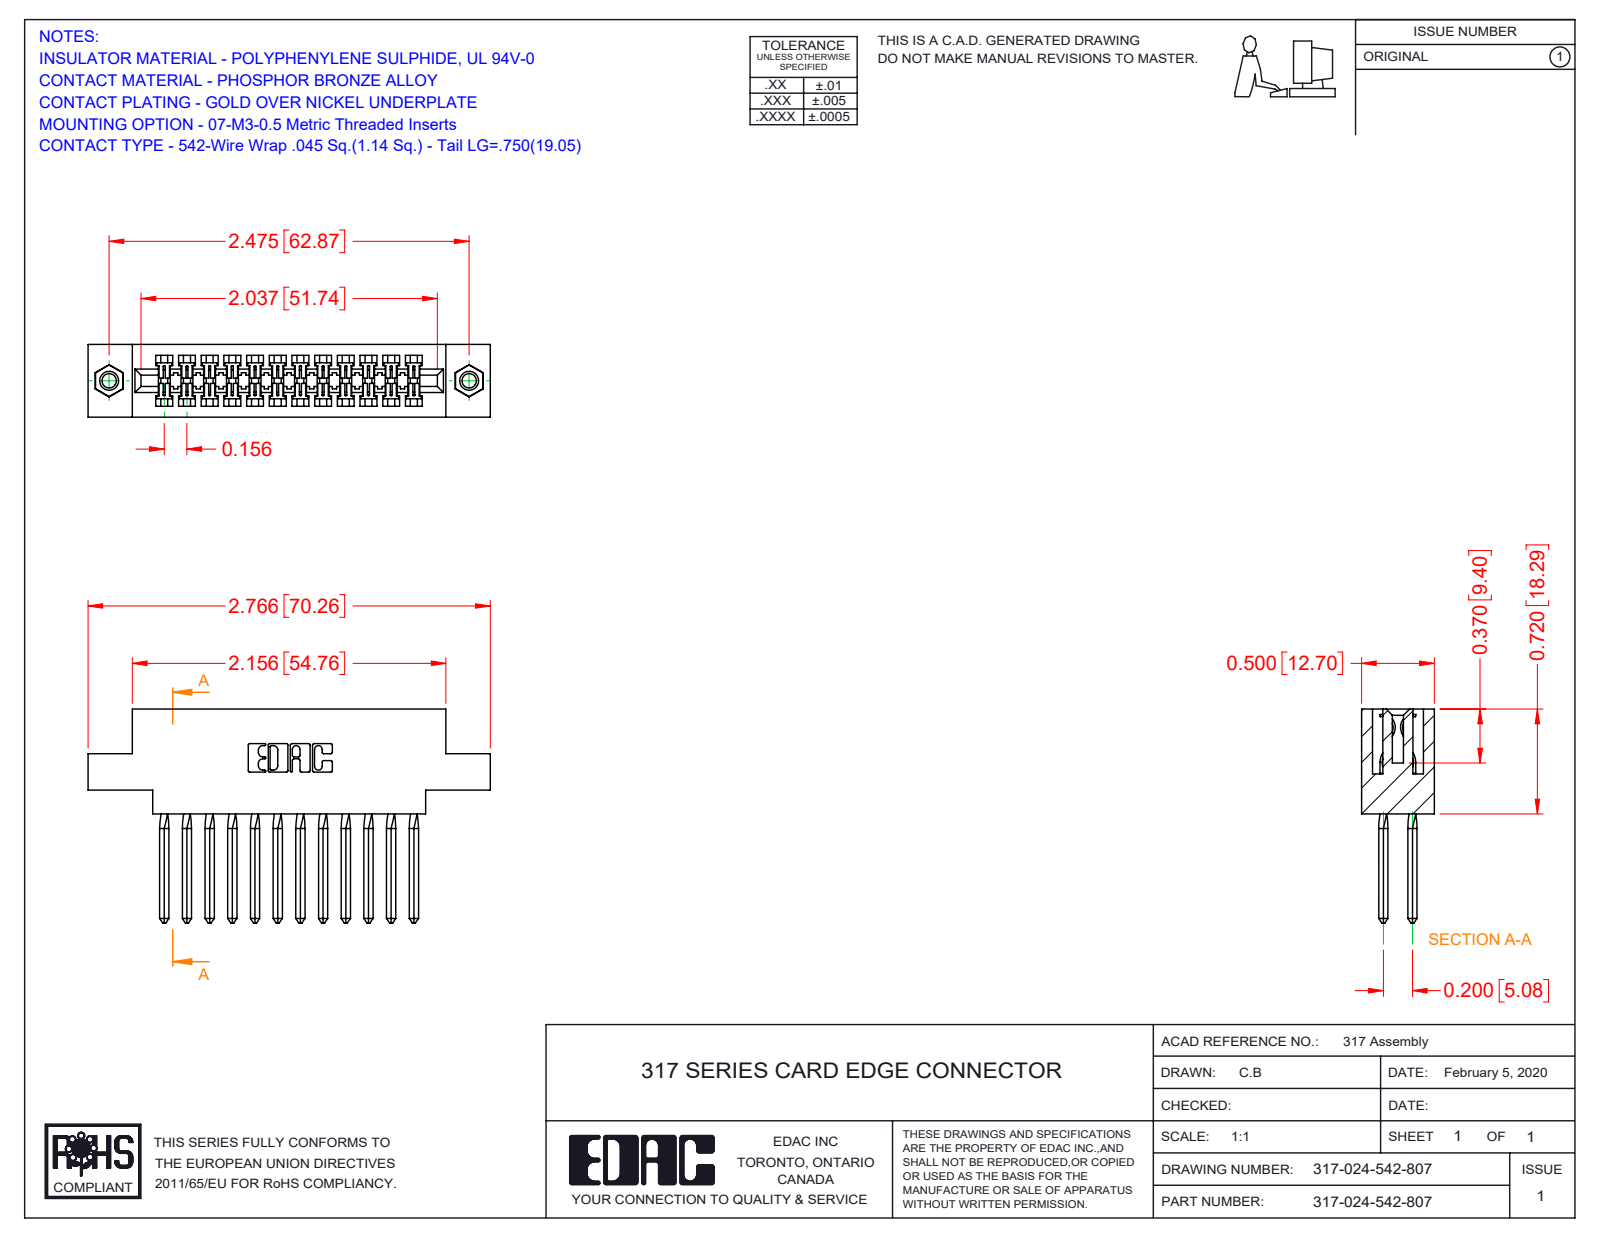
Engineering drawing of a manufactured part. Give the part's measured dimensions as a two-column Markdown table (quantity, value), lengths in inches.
| quantity | value |
| --- | --- |
| part name | 317 Part_.156 Dia - TI; 317-290-003_542; 317-024-542-807; 345-250-001_345-250-005-103 |
| STEP written by | SolidWorks 2016 (CONFIG_CONTROL_DESIGN) |
| units | inches |
| bodies | 27 solids, 1530 faces (1194 planar, 224 cylindrical, 112 other) |
| overall size | 2.766 × 1.47 × 0.5 |
| volume | 0.643 in³ |
| surface area | 21.29 in² |
| round holes (diameter × count) | 0.098 × 2, 0.125 × 2, 0.156 × 2 |
| round bosses / shafts (diameter × count) | 0.155 × 2 |
| partial cylindrical surfaces (radius × count) | 0.006 × 48, 0.01 × 22, 0.007 × 6, 0.031 × 6, 0.026 × 3, 0.074 × 2, 0.089 × 2, 0.1 × 2 |
| main face-to-face distances | 0.5, 0.075, 0.425, 0.11, 0.35, 0.22, 0.116, 0.2, 0.136, 0.156 |
| hole center spacings | 2.475 |
